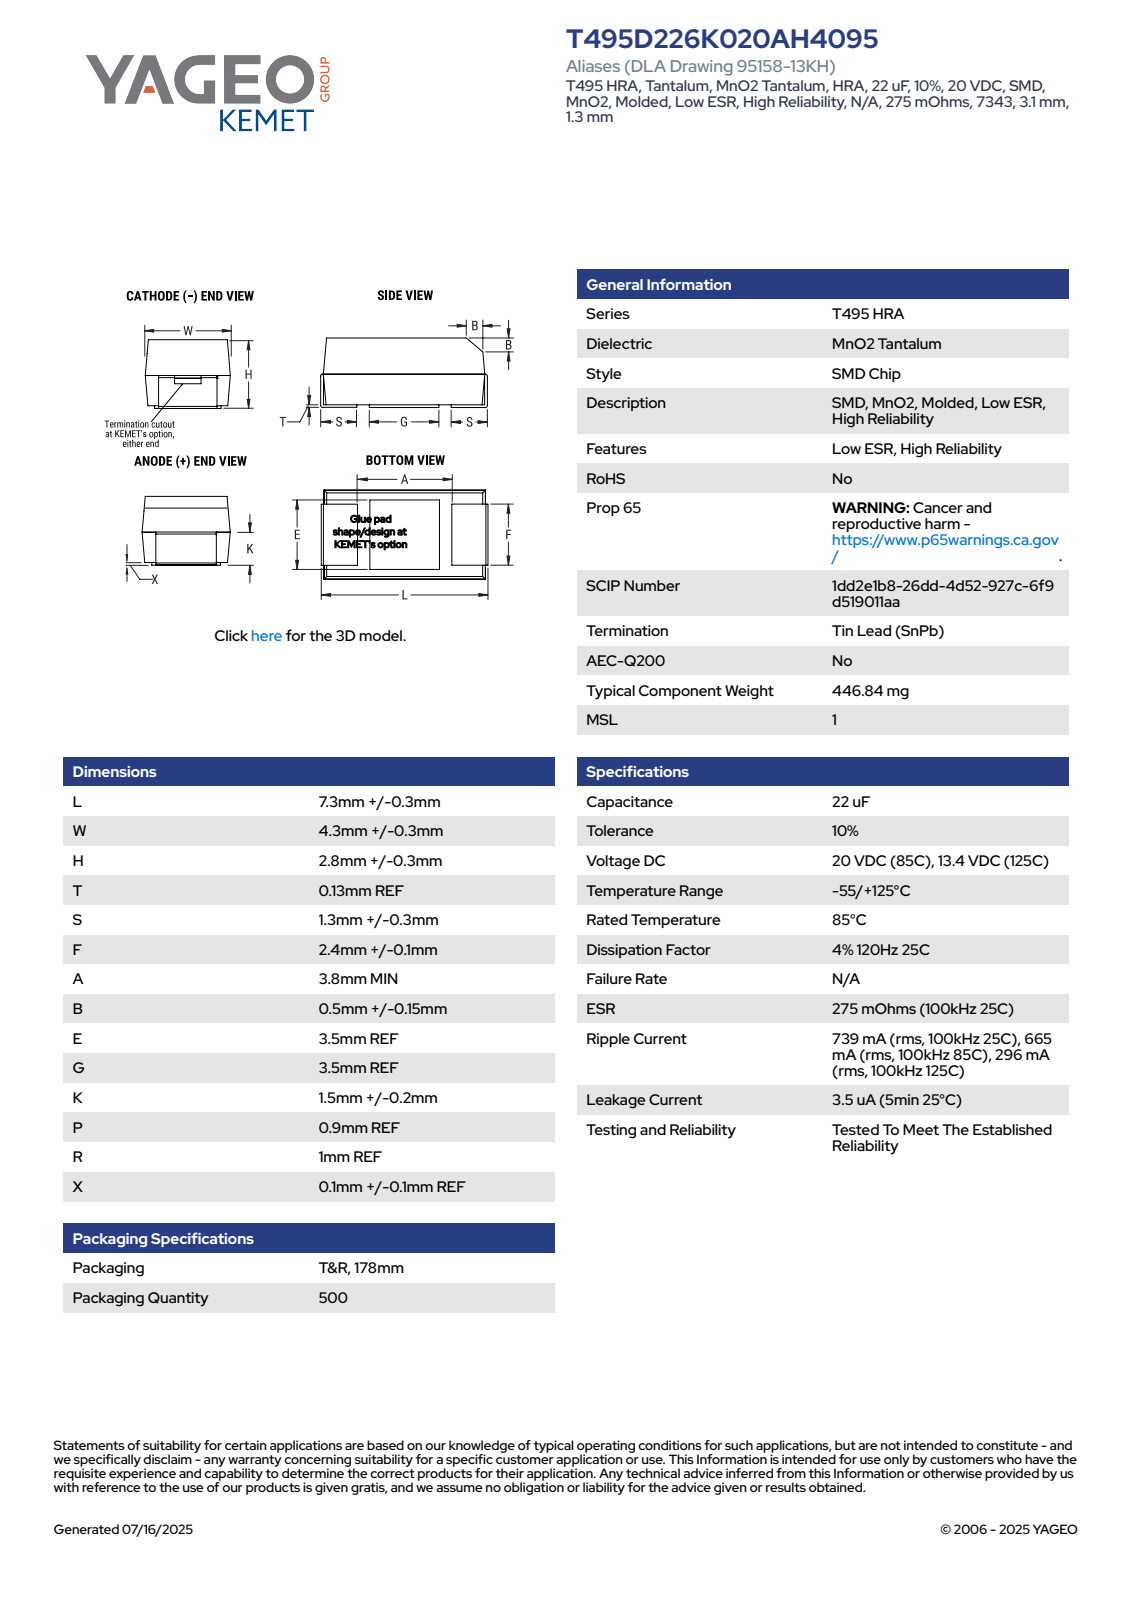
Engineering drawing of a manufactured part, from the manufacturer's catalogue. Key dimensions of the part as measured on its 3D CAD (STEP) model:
Part name (STEP PRODUCT): CTSM_7343_L7.60W4.6H3.10S1.3F2.4R1P0.9B0.5K1.5; CTSM_Case_Bottom_29; CTSM_Case_Top_29; CTSM_Case_Cathode_29 (+1 more)
STEP written by: SolidWorks 2014 (AUTOMOTIVE_DESIGN)
Units: millimetres
Bodies: 7 solids, 100 faces (95 planar, 5 cylindrical, 0 other)
Overall size (bounding box): 7.6 × 4.6 × 3.1
Volume: 97 mm³ · Surface area: 227 mm²
Main face-to-face distances: 1.6, 1.37, 2.97, 4.58, 7.31, 1.47, 3.07, 1.5, 3.1, 7.47
